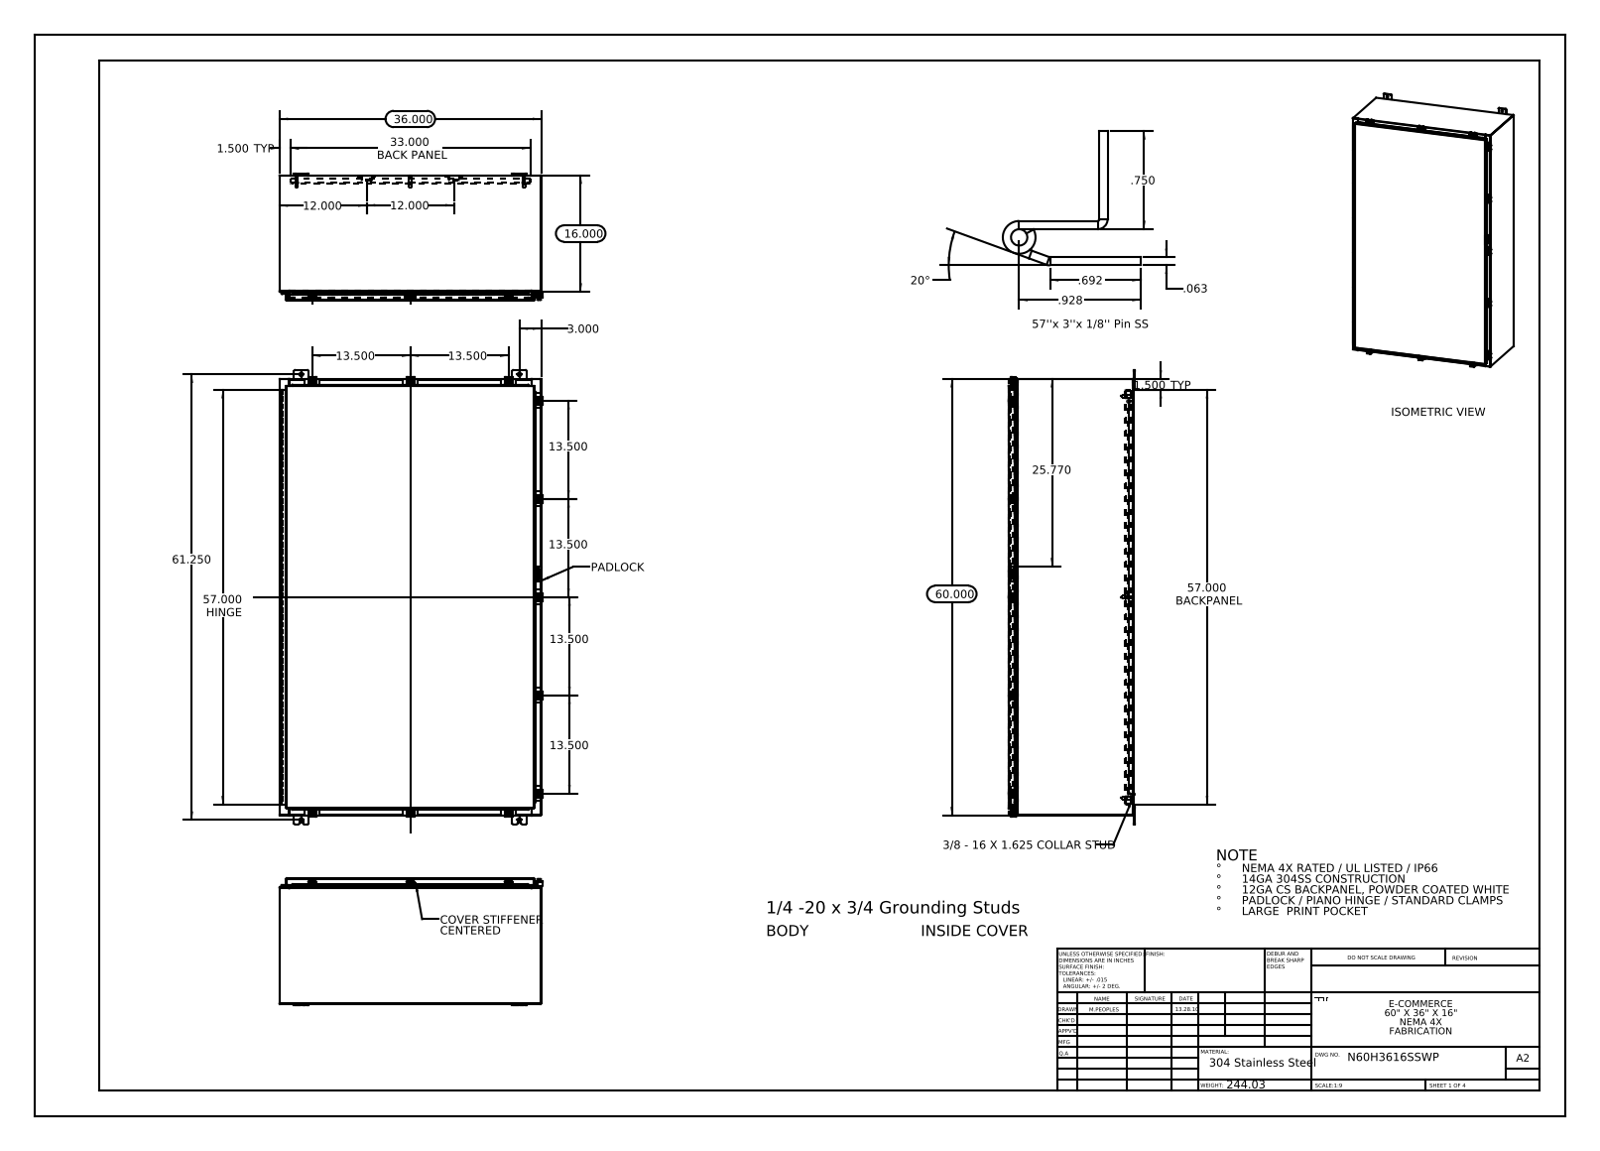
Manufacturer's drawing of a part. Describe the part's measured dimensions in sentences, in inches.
The part is named "N60H3616SSWP Cover; N60H3616SSWP Door Stiffener; N60H3616SSWP Clamp Top; N60H3616SSWP Mounting Feet (+8 more)". Its 3-D file was written by "SolidWorks 2013 (CONFIG_CONTROL_DESIGN)". It is 79 solids with 3408 faces: 1766 planar, 1466 cylindrical and 176 other. Overall it measures 62.5 by 36.211 by 17.389 inches. Its volume is 853.2 cubic inches and its surface area 21 384 square inches. Round holes: 12 of diameter 0.5, 11 of diameter 0.213, 11 of diameter 0.26, 8 of diameter 0.25, 2 of diameter 0.125, 1 of diameter 0.125. Round bosses or shafts: 12 of diameter 0.25, 11 of diameter 0.5, 11 of diameter 0.399, 8 of diameter 0.625, 8 of diameter 0.375, 8 of diameter 0.33. Partial cylindrical surfaces (rounded edges, fillets, slot ends): 50 of radius 0.06, 39 of radius 0.013, 33 of radius 0.088, 24 of radius 0.19, 22 of radius 0.12, 22 of radius 0.141, 17 of radius 0.05, 16 of radius 0.08. The main face-to-face distances are 0.075, 17.126, 17.051, 0.104, 17.201, 35.925, 16.126, 1, 1.075, 16.051. The hole center spacings are 13.5, 13.663, 2.225, 27, 27.625, 29.802, 41.709, 57.39.
